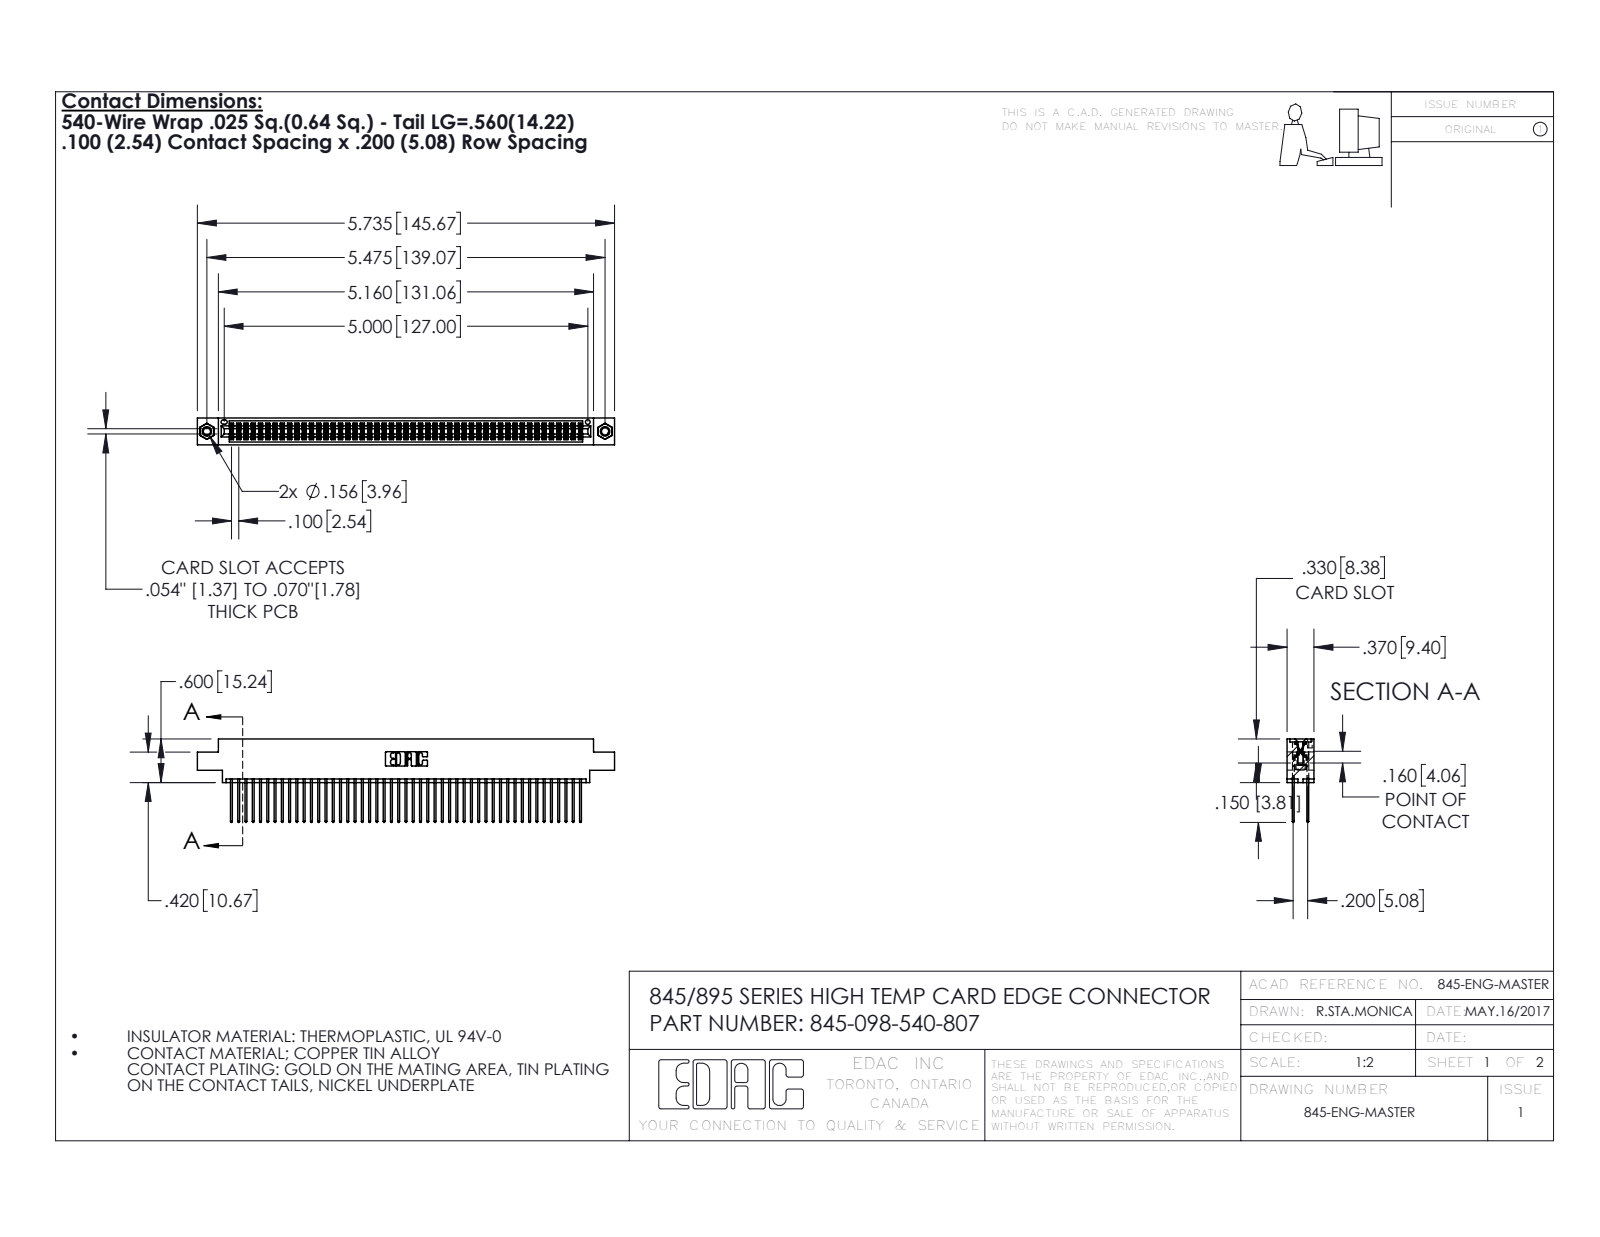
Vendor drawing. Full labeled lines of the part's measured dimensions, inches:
Part name (STEP PRODUCT): 345-250-001_345-250-005-103; 345-292-001_345-293-140; 345-098-540-807; 345 Part_0.170 Offset - 0.156 Dia-TI
STEP written by: SolidWorks 2016 (CONFIG_CONTROL_DESIGN)
Units: inches
Bodies: 101 solids, 5090 faces (3350 planar, 1724 cylindrical, 16 other)
Overall size (bounding box): 5.735 × 1.147 × 0.37
Volume: 0.882 in³ · Surface area: 36.28 in²
Round holes (diameter × count): ⌀0.098 ×2, ⌀0.125 ×2, ⌀0.156 ×2, ⌀0.064 ×1
Round bosses / shafts (diameter × count): ⌀0.155 ×2
Partial cylindrical surfaces — rounded edges, fillets, slot ends (radius × count): R0.006 ×147, R0.01 ×98, R0.01 ×22, R0.007 ×6, R0.031 ×6, R0.026 ×3, R0.014 ×2, R0.019 ×2
Main face-to-face distances: 0.072, 0.298, 0.2, 0.098, 0.272, 0.025, 0.37, 0.225, 0.175, 0.149
Hole centre spacings: 0.27, 5.239, 5.475
